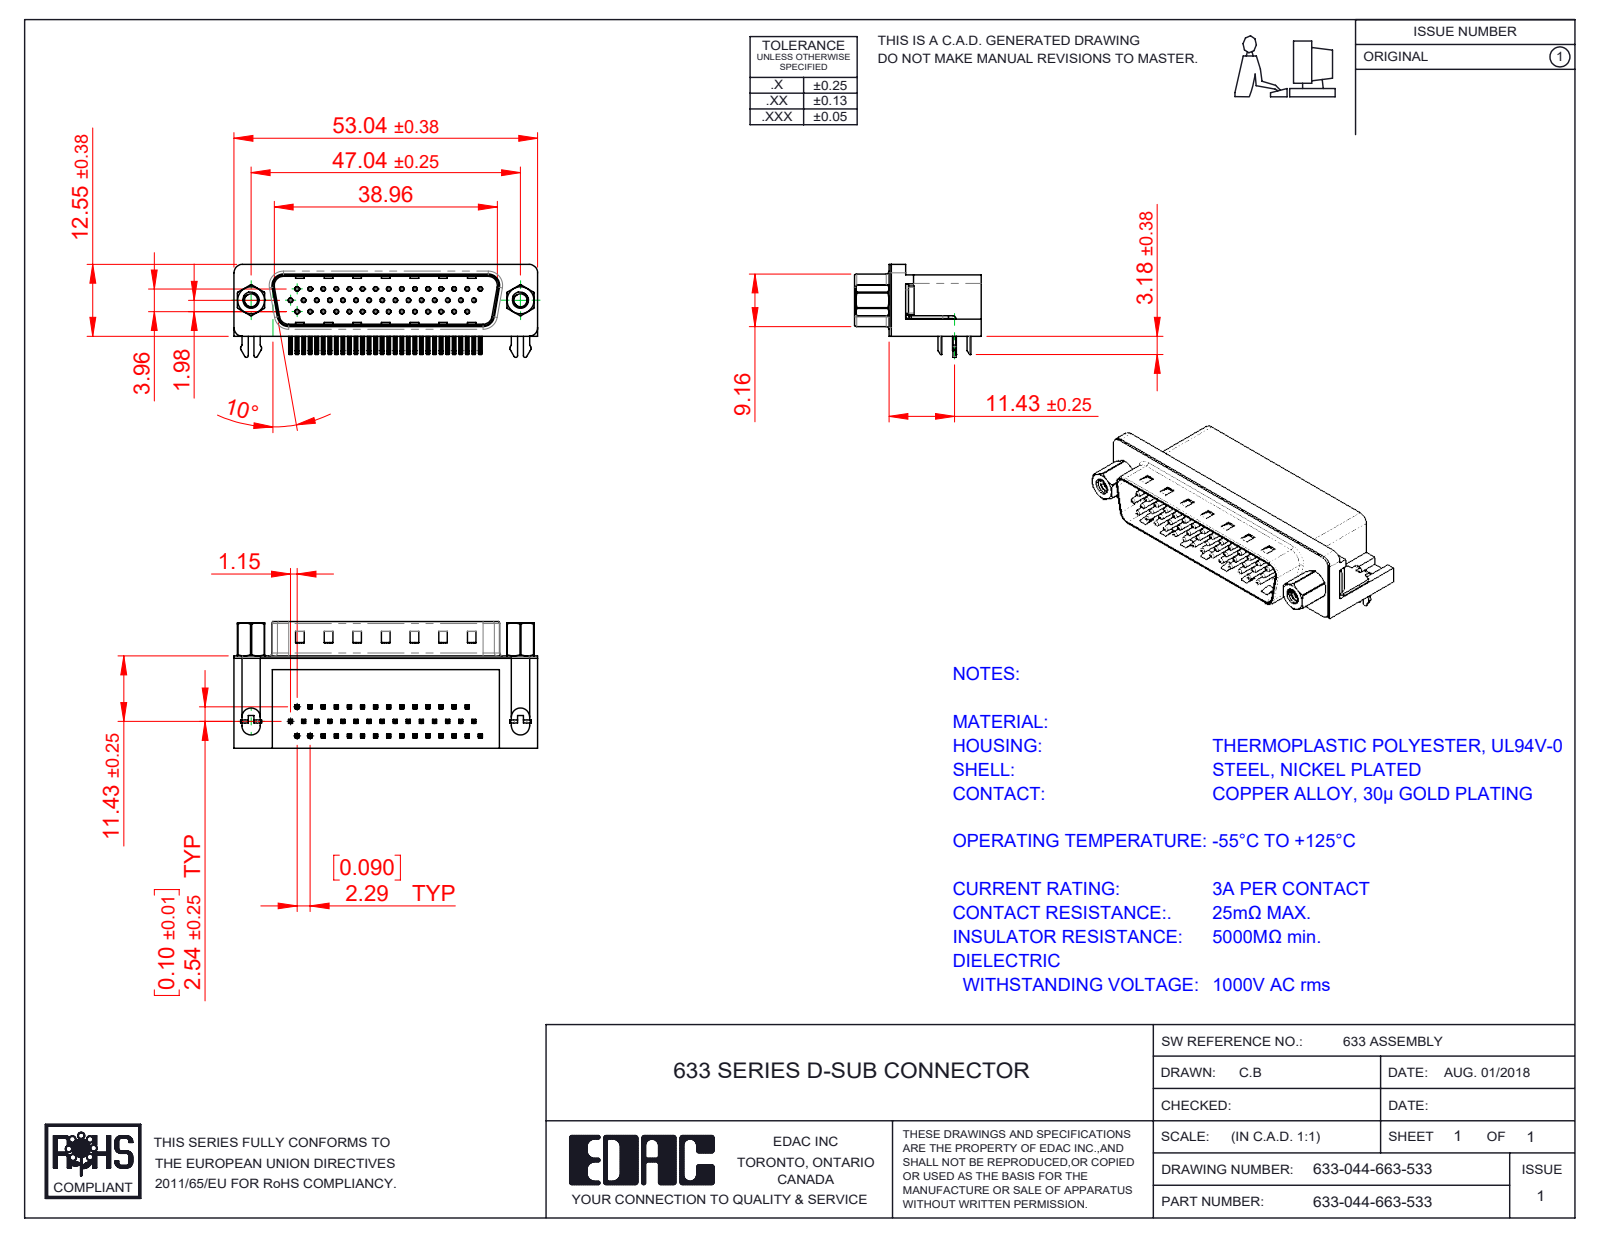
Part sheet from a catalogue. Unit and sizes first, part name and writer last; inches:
Units: inches
Overall size (bounding box): 2.088 × 0.87 × 0.64
Round holes (diameter × count): ⌀0.014 ×44, ⌀0.031 ×44, ⌀0.089 ×2, ⌀0.09 ×2, ⌀0.157 ×2, ⌀0.189 ×2, ⌀0.197 ×2
Round bosses / shafts (diameter × count): ⌀0.03 ×44, ⌀0.193 ×2, ⌀0.187 ×2, ⌀0.154 ×2, ⌀0.11 ×2
Partial cylindrical surfaces — rounded edges, fillets, slot ends (radius × count): R0.01 ×184, R0.005 ×88, R0.039 ×16, R0.02 ×14, R0.063 ×8, R0.059 ×7, R0.013 ×4, R0.035 ×4
Main face-to-face distances: 0.016, 0.407, 0.618, 0.345, 0.114, 0.098, 0.634, 0.083, 0.421, 0.1
Hole centre spacings: 0.09, 0.18, 0.18, 0.09, 0.27, 0.361, 0.451, 0.089
Volume: 0.507 in³ · Surface area: 16.55 in²
Bodies: 52 solids, 3850 faces (2371 planar, 1132 cylindrical, 347 other)
Part name (STEP PRODUCT): 633 Shell_44 Contact; 633 4-40 Hex Standoff; 633 4-40 Threaded Rivet; 633-044-663-533 (+5 more)
STEP written by: SolidWorks 2016 (CONFIG_CONTROL_DESIGN)
